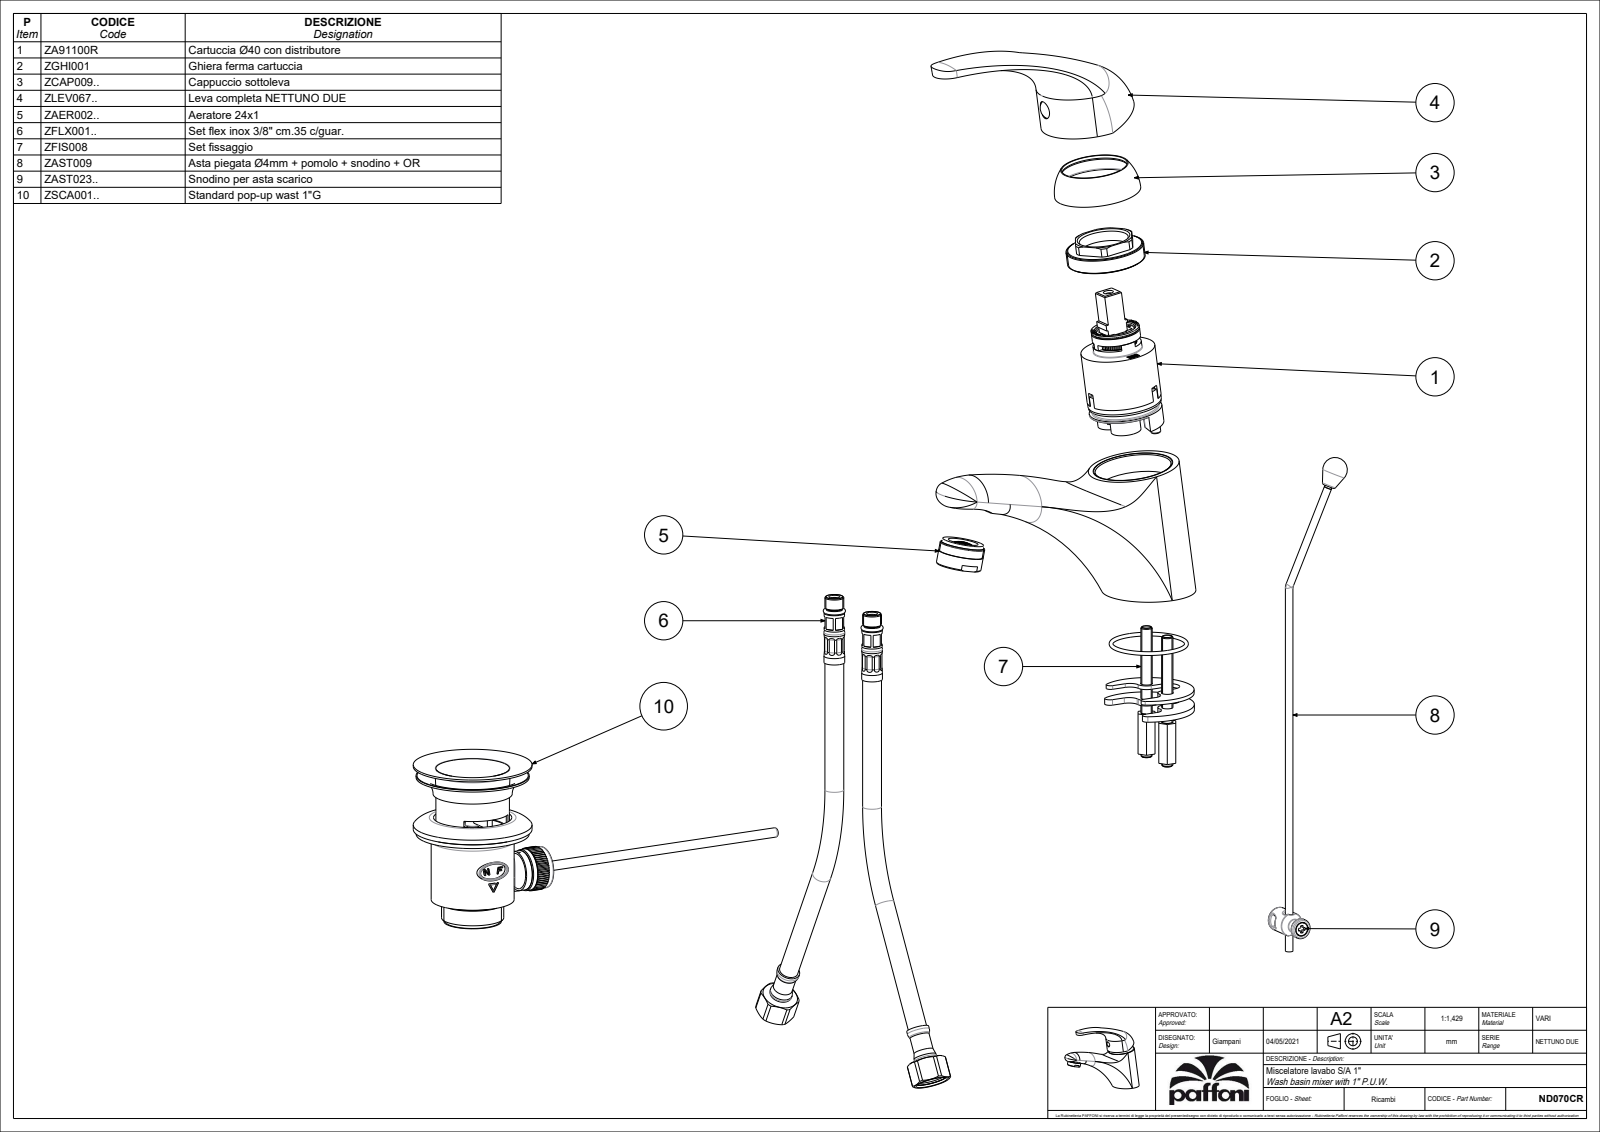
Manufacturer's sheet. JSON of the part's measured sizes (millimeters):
{"part_name": "ND070CR", "step_written_by": "CREO PARAMETRIC BY PTC INC, 2020044 (CONFIG_CONTROL_DESIGN)", "units": "millimeters", "bodies": {"solids": 1, "faces": 194, "planar": 60, "cylindrical": 52, "other": 82}, "overall_size": [168.47, 117.58, 51], "volume_mm3": 211053, "surface_area_mm2": 54660, "round_holes": [[5, 3], [5.5, 2], [7, 2], [9, 2], [11, 2], [40.5, 2], [6, 1], [24.5, 1], [35, 1], [39.1, 1], [42.5, 1]], "round_bosses_or_shafts": [[37.5, 1], [24, 1], [5, 1], [4, 1]], "partial_cylinders_radius": [[3.9, 1], [4, 1]], "face_to_face_distances": [60.94, 60.98, 1.5, 15.3, 76.22, 15.28, 15.24, 46.48, 14.46, 14.5], "hole_center_spacings": [8.6, 15.62, 8.59, 11.49, 11.81, 13.46, 15.63, 15.81]}
